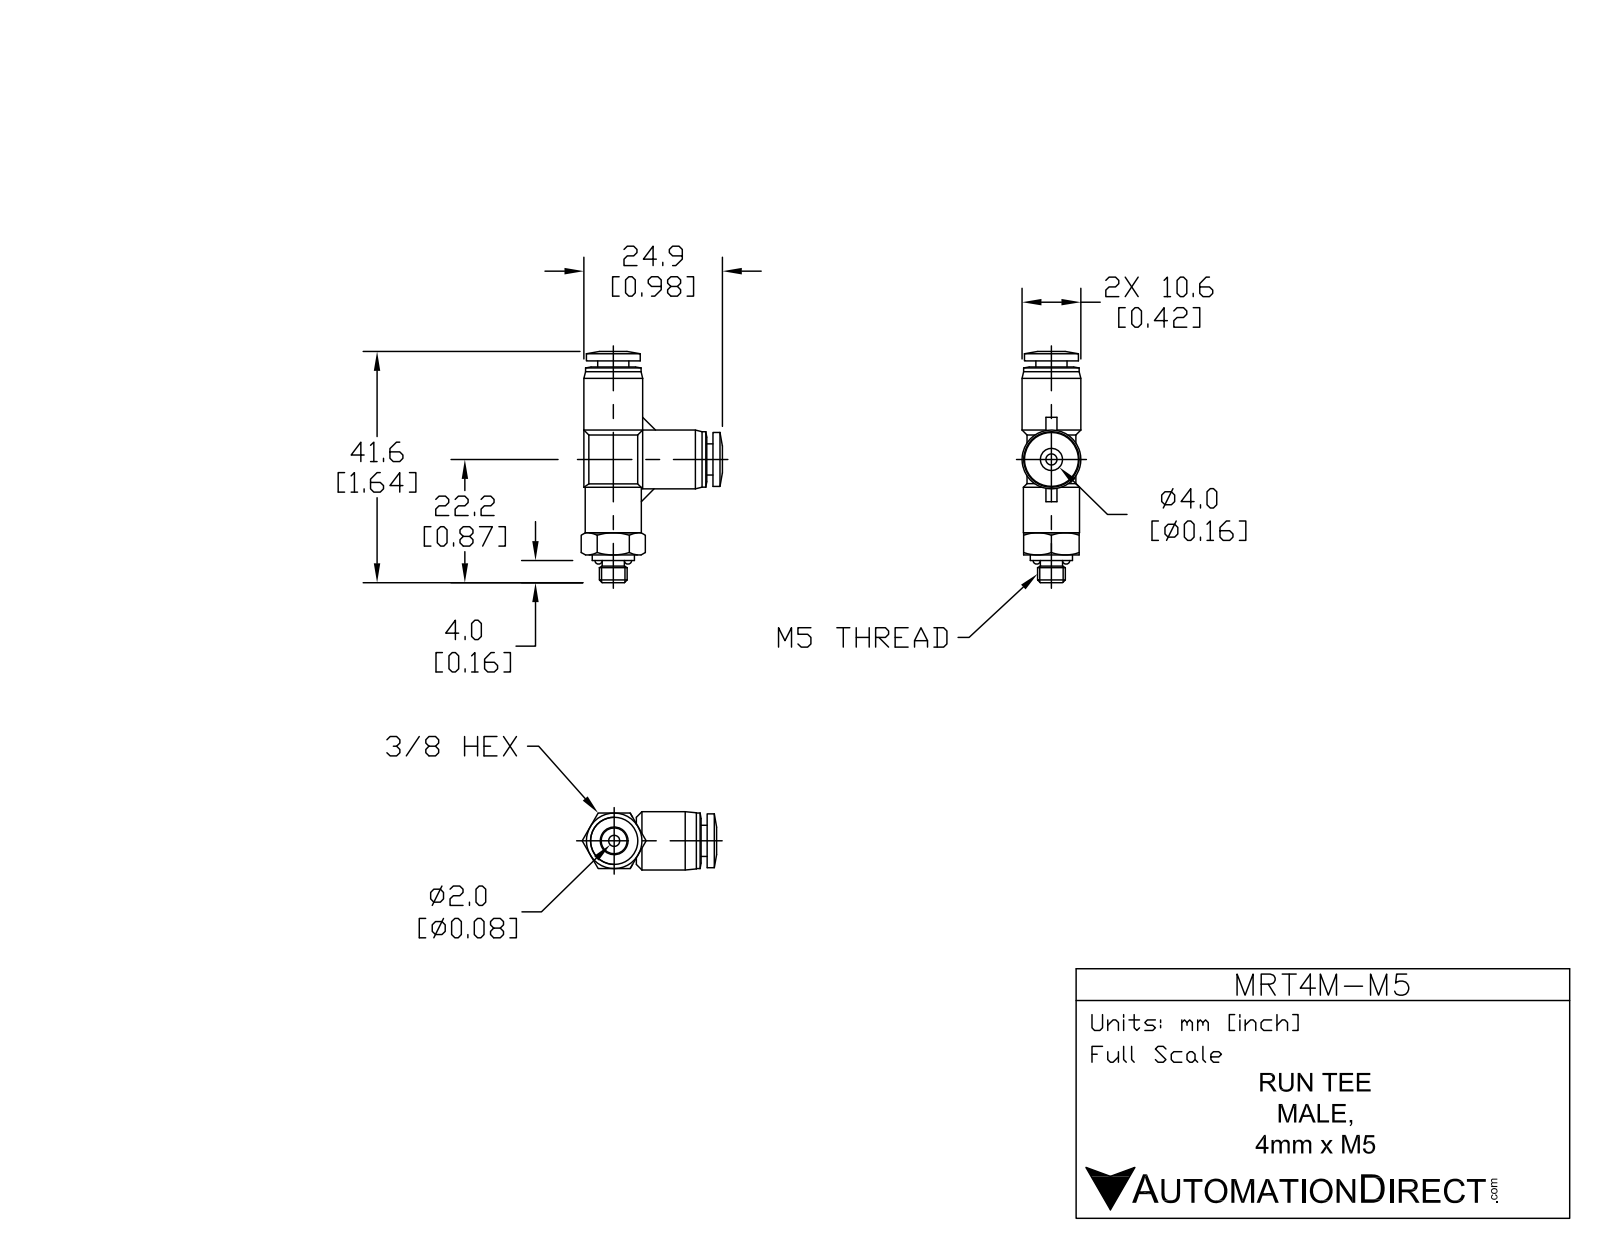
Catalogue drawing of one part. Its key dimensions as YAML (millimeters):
part_name: "MRT4M-M5"
step_written_by: "SolidWorks 2015 (AUTOMOTIVE_DESIGN)"
units: millimeters
bodies: {solids: 2, faces: 119, planar: 28, cylindrical: 40, other: 51}
overall_size: [40.9, 25.2, 10.6]
volume: 3520
surface_area: 2800
round_holes:
  - {diameter: 2.5, count: 2}
  - {diameter: 4.3, count: 2}
round_bosses_or_shafts:
  - {diameter: 10.6, count: 2}
  - {diameter: 10, count: 2}
  - {diameter: 9.7, count: 2}
  - {diameter: 8.8, count: 2}
  - {diameter: 5.6, count: 2}
  - {diameter: 10.1, count: 1}
  - {diameter: 7.6, count: 1}
  - {diameter: 5, count: 1}
face_to_face_distances: [10, 1.1, 4, 34.2, 6, 33.1, 12, 13.1, 33.4, 34.4]
